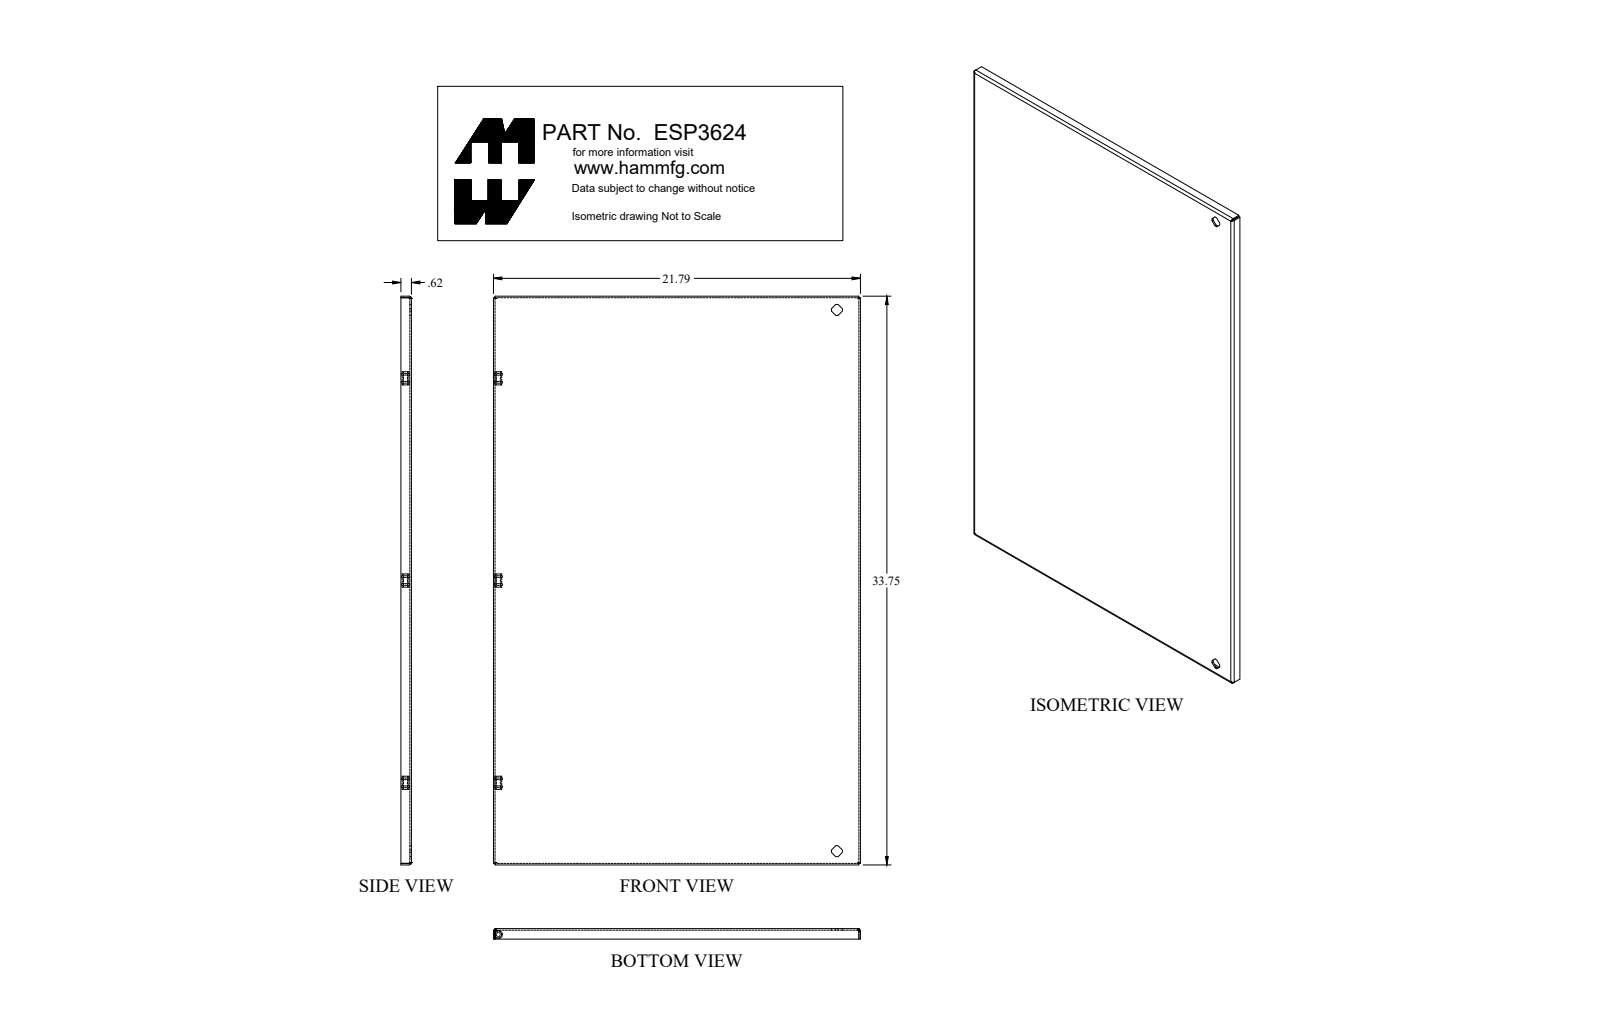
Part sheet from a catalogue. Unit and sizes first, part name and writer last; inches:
Units: inches
Overall size (bounding box): 33.75 × 23.706 × 9.953
Round holes (diameter × count): ⌀0.136 ×3, ⌀0.242 ×3, ⌀0.516 ×2
Round bosses / shafts (diameter × count): ⌀0.232 ×6, ⌀0.356 ×3, ⌀0.788 ×2, ⌀0.535 ×2, ⌀0.496 ×2, ⌀0.435 ×2
Partial cylindrical surfaces — rounded edges, fillets, slot ends (radius × count): R0.048 ×28, R0.01 ×24, R0.036 ×6, R0.108 ×6, R0.06 ×4, R0.143 ×4, R0.153 ×4, R0.156 ×4
Main face-to-face distances: 0.095, 0.072, 22.008, 0.038, 22.08, 0.78, 0.875, 0.852, 0.947, 21.936
Hole centre spacings: 13, 26, 32.159
Volume: 95.9 in³ · Surface area: 2 281 in²
Bodies: 14 solids, 634 faces (376 planar, 190 cylindrical, 68 other)
Part name (STEP PRODUCT): ESP3624
STEP written by: SolidWorks 2018 (AUTOMOTIVE_DESIGN)
